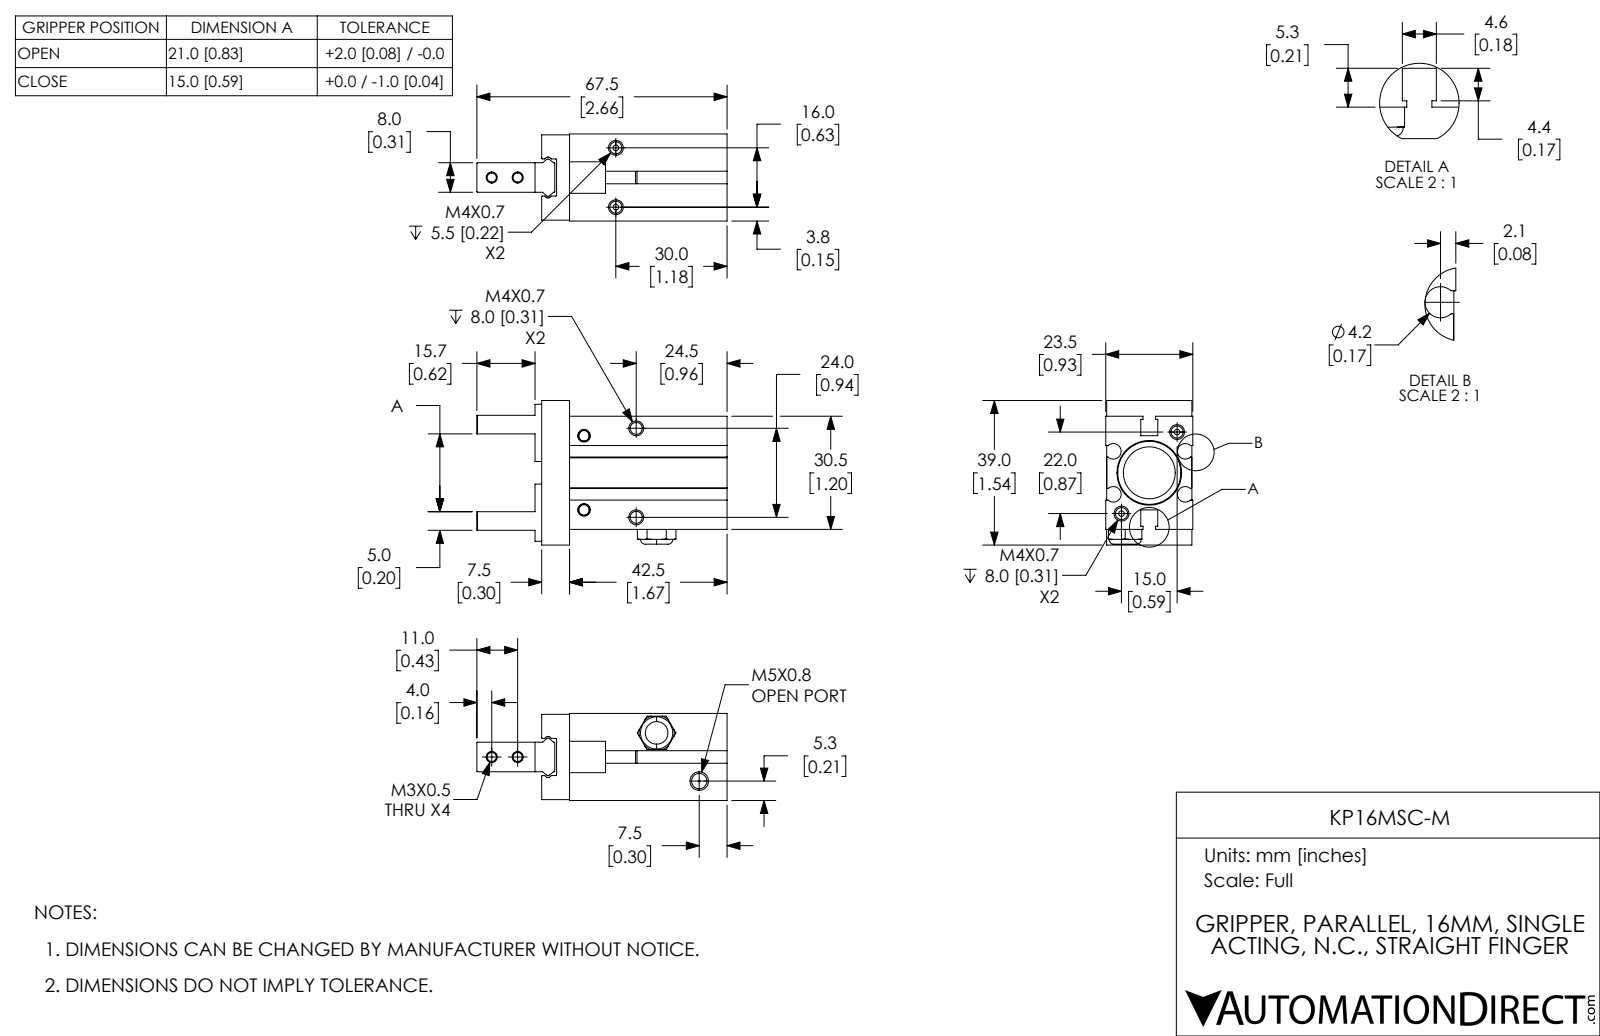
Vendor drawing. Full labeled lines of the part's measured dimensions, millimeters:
Part name (STEP PRODUCT): KP16MSC-M; KP16MSC-M-3; KP16MSC-M-2; KP16MSC-M-1
STEP written by: SolidWorks 2017 (CONFIG_CONTROL_DESIGN)
Units: millimetres
Bodies: 3 solids, 263 faces (125 planar, 68 cylindrical, 70 other)
Overall size (bounding box): 67.5 × 39 × 23.5
Volume: 30 425 mm³ · Surface area: 13 538 mm²
Round holes (diameter × count): ⌀3.24 ×6, ⌀0.5 ×2, ⌀2.46 ×2, ⌀4.02 ×2, ⌀4.13 ×2, ⌀6.1 ×1, ⌀14 ×1, ⌀17 ×1
Partial cylindrical surfaces — rounded edges, fillets, slot ends (radius × count): R0.2 ×10, R2.1 ×4, R0.4 ×2, R0.5 ×2, R1 ×2
Main face-to-face distances: 7.5, 15.75, 30.5, 4, 23.2, 15.7, 23.5, 3.5, 16, 7.2
Hole centre spacings: 13.31, 27.68, 34.44, 7, 11.1, 16, 17.36, 18.2
